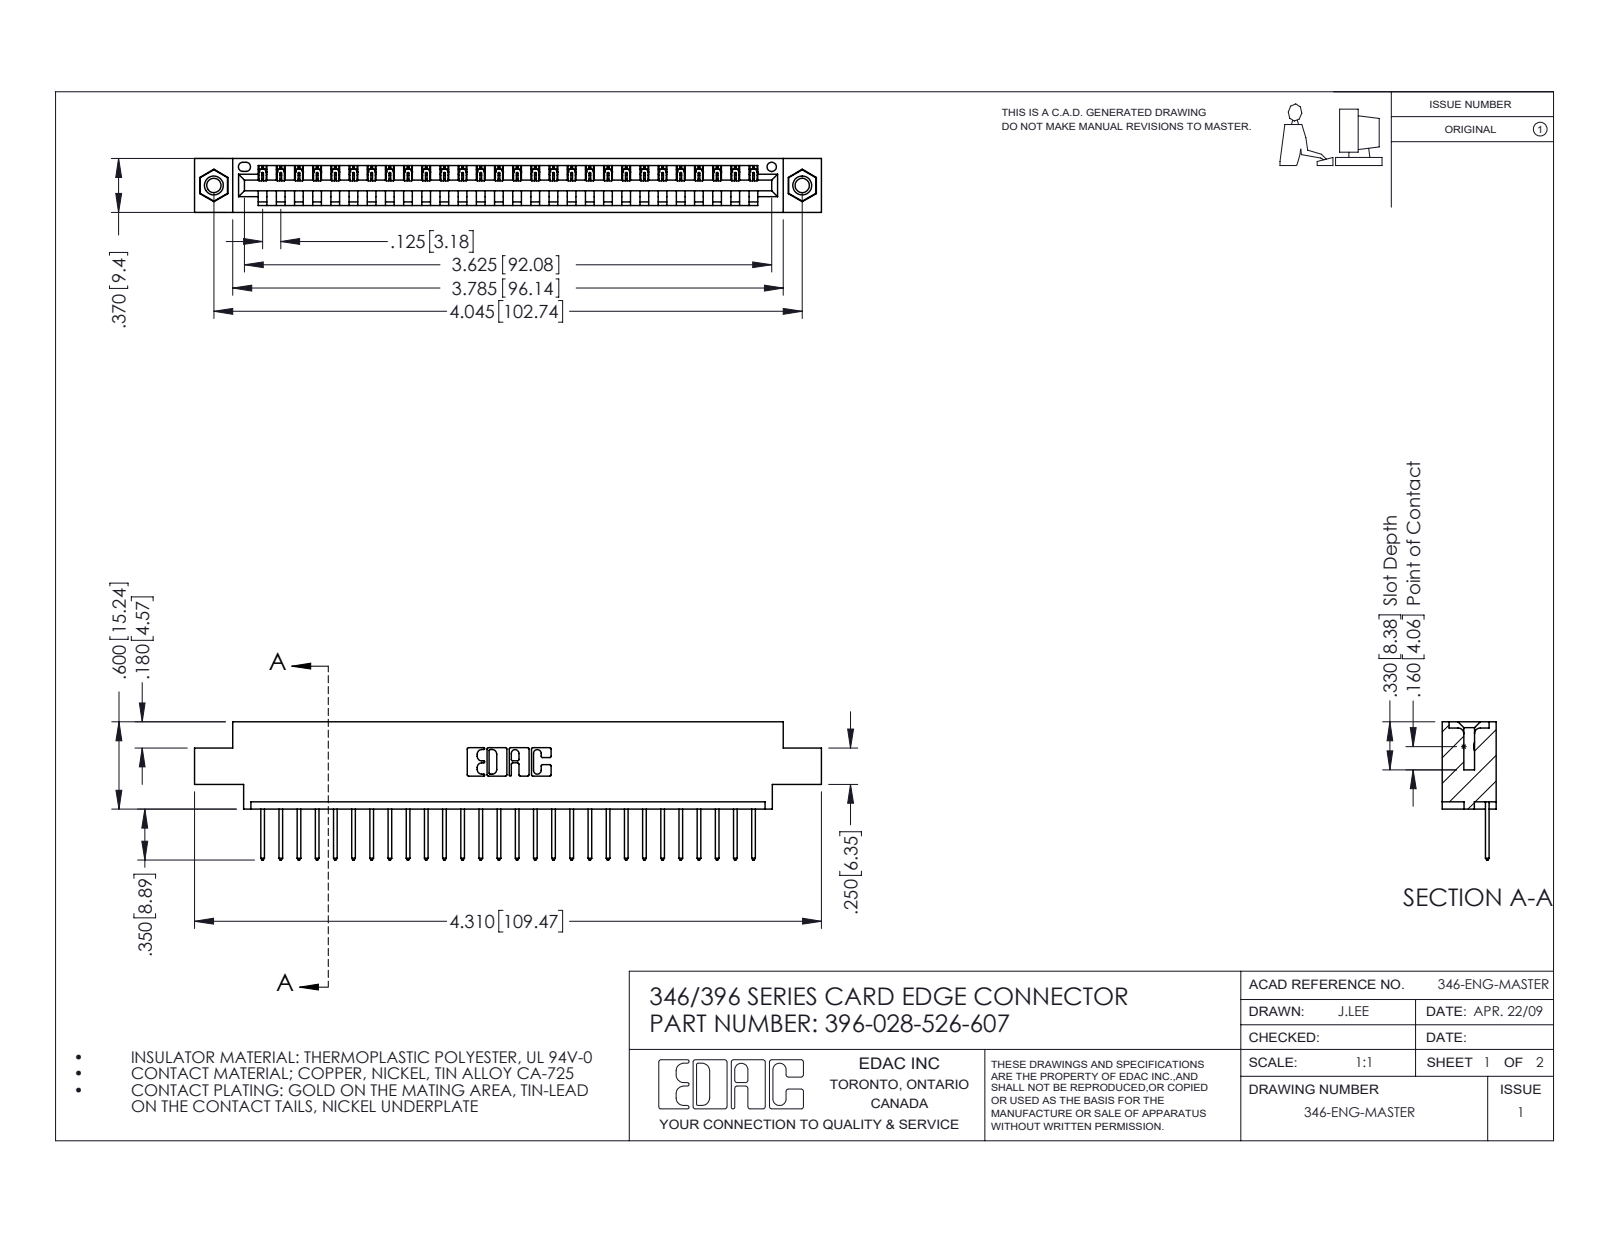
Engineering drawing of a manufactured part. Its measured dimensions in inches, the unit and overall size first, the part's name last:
Units: inches
Overall size (bounding box): 4.31 × 0.95 × 0.37
Round holes (diameter × count): ⌀0.098 ×2, ⌀0.125 ×2, ⌀0.156 ×2, ⌀0.064 ×1
Round bosses / shafts (diameter × count): ⌀0.155 ×2
Partial cylindrical surfaces — rounded edges, fillets, slot ends (radius × count): R0.006 ×56, R0.01 ×56, R0.01 ×22, R0.007 ×6, R0.031 ×6, R0.026 ×3, R0.031 ×2, R0.04 ×2
Main face-to-face distances: 0.048, 0.322, 0.37, 0.25, 0.072, 0.298, 0.025, 0.222, 0.148, 0.1
Hole centre spacings: 0.246, 3.837, 4.045
Volume: 0.622 in³ · Surface area: 19.77 in²
Bodies: 31 solids, 1810 faces (1232 planar, 562 cylindrical, 16 other)
Part name (STEP PRODUCT): 396-028-526-607; 345-250-001_345-250-005-103; 345-292-001_345-293-126; 346 Part_0.170 Offset - 0.156 Dia-TI
STEP written by: SolidWorks 2016 (CONFIG_CONTROL_DESIGN)
